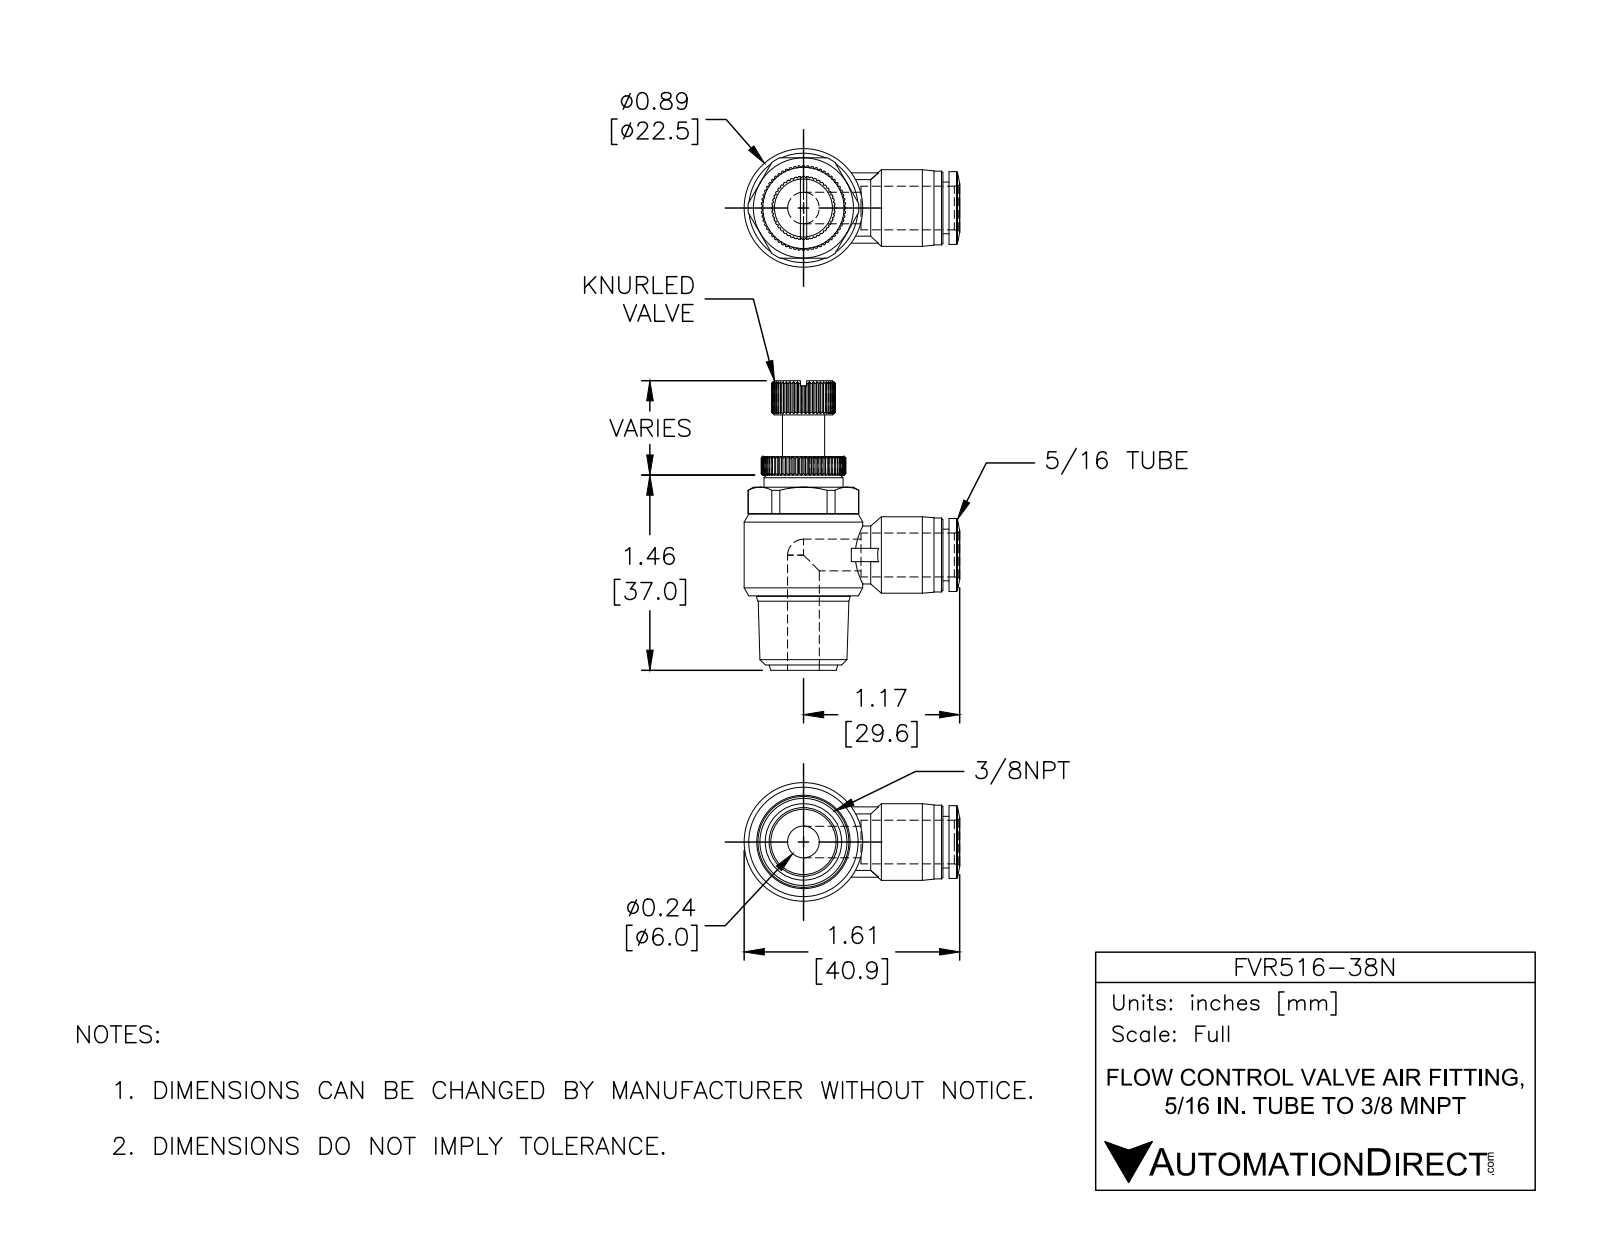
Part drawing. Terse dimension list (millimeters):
name: FVR516-38N
written by: SolidWorks 2015 (CONFIG_CONTROL_DESIGN)
unit: mm
bodies: 1 solid, 558 faces (252 planar, 144 cylindrical, 162 other)
size: 54.9 × 40.8 × 22.5
volume: 13 700 mm³; area: 5 928 mm²
holes: 2× ⌀6, 1× ⌀8.3
bosses: 1× ⌀22.5, 1× ⌀19, 1× ⌀17.2, 1× ⌀15, 1× ⌀14.5, 1× ⌀14, 1× ⌀13.8, 1× ⌀11
rounds: 1× R6, 1× R8, 1× R10.5
face distances: 19, 20.6, 5.8, 26.4, 14.1, 34.7, 40.5, 10.9, 54.9, 40.8
